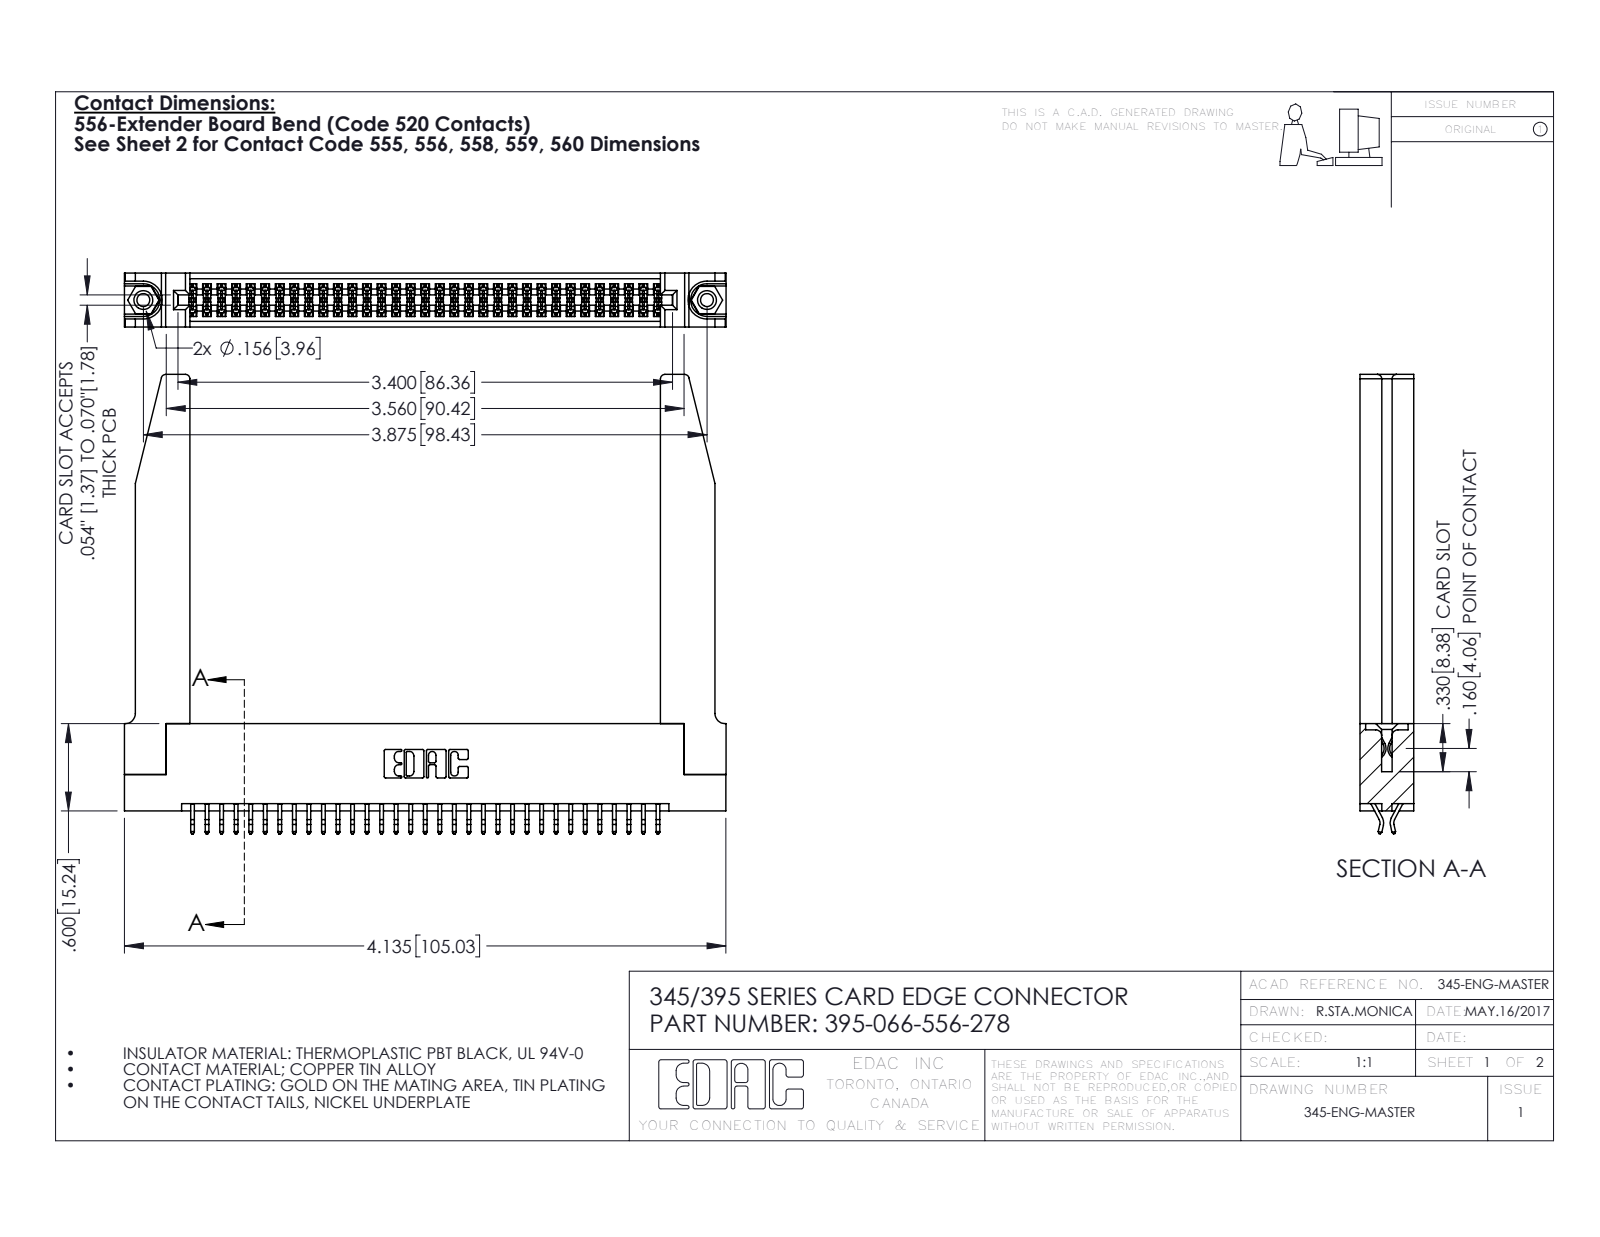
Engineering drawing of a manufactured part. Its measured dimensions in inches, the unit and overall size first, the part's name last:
Units: inches
Overall size (bounding box): 4.136 × 3.157 × 0.37
Round holes (diameter × count): ⌀0.089 ×2, ⌀0.125 ×2, ⌀0.156 ×2, ⌀0.064 ×1
Round bosses / shafts (diameter × count): ⌀0.155 ×2
Partial cylindrical surfaces — rounded edges, fillets, slot ends (radius × count): R0.006 ×99, R0.01 ×22, R0.03 ×8, R0.007 ×6, R0.031 ×6, R0.026 ×3, R0.01 ×2, R0.014 ×2
Main face-to-face distances: 0.37, 0.072, 0.298, 0.2, 0.025, 0.098, 0.272, 0.225, 0.148, 0.15
Hole centre spacings: 0.27, 3.64, 3.875
Volume: 1.092 in³ · Surface area: 33.42 in²
Bodies: 71 solids, 4056 faces (2664 planar, 1340 cylindrical, 52 other)
Part name (STEP PRODUCT): 345 Part_Flush Mounting Lugs - 0.156 Dia-TH; 345-220-078_345-220-078; 345-292-001_556 Tail; 345-250-001_345-250-001-102 (+1 more)
STEP written by: SolidWorks 2016 (CONFIG_CONTROL_DESIGN)
